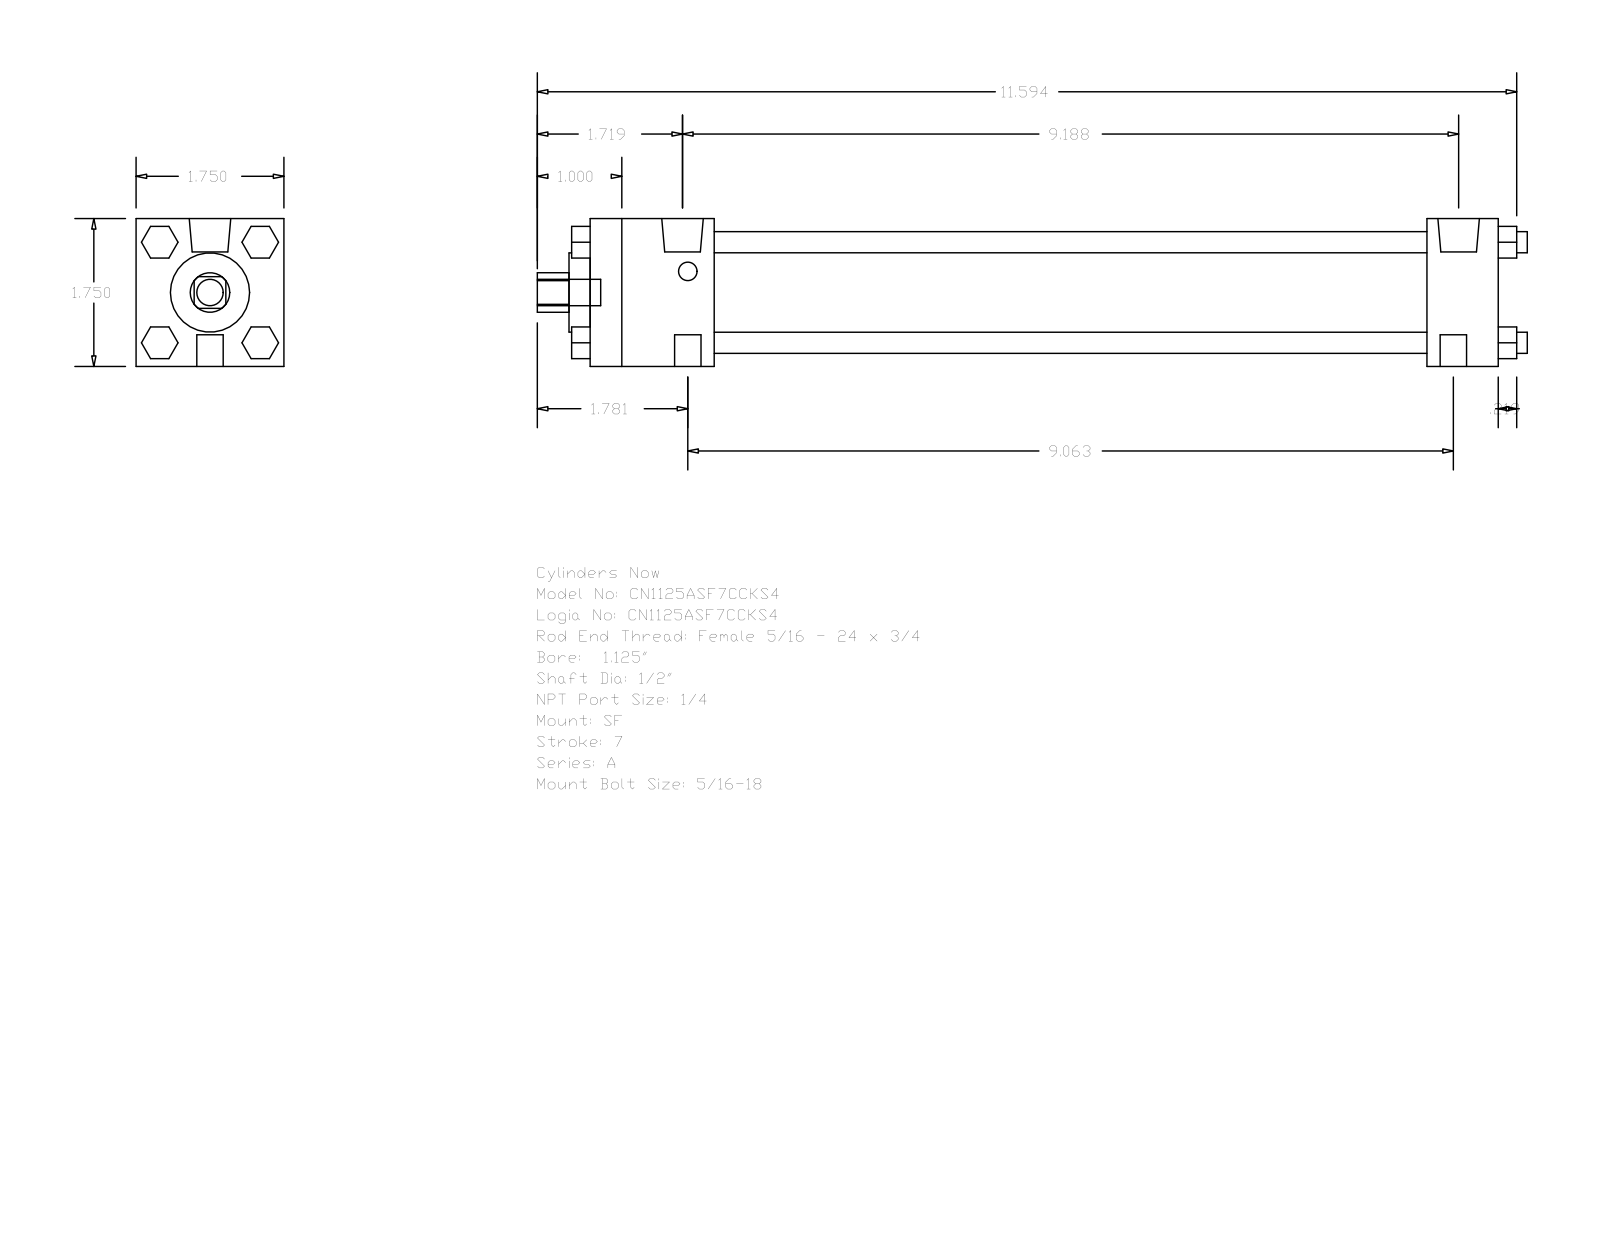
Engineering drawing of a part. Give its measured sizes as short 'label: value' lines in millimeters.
name: A_SF__0112_0.5
written by: GSSL Pune (CONFIG_CONTROL_DESIGN)
unit: mm
bodies: 0 solids, 120 faces (92 planar, 28 cylindrical, 0 other)
size: 297.66 × 44.45 × 44.45
holes: 1× ⌀12.7, 1× ⌀23.81, 1× ⌀31.88
bosses: 4× ⌀6.35, 3× ⌀7.94, 2× ⌀12.49, 2× ⌀5.56
rounds: 1× R5.94
face distances: 44.46, 273.05, 251.61, 21.44, 37.3, 214.31, 235.75, 9.53, 5.59, 9.52
